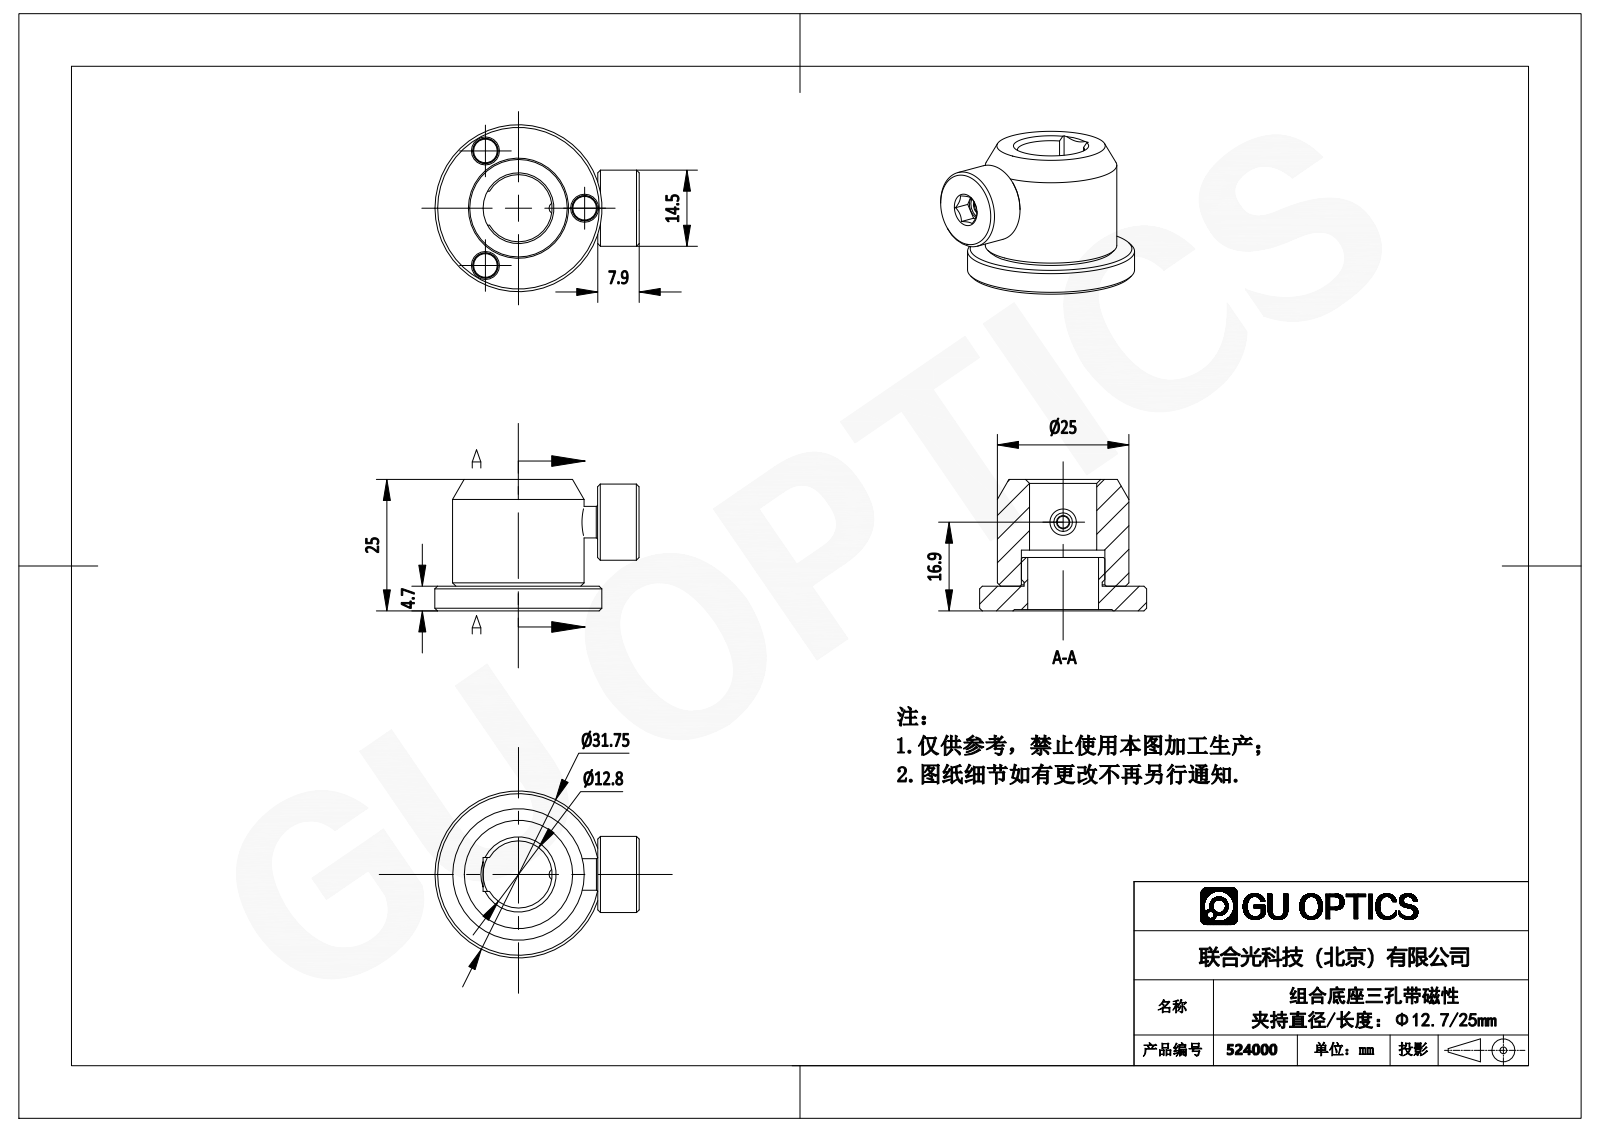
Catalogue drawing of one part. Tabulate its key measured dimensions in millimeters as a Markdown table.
| quantity | value |
| --- | --- |
| part name | 524000 |
| STEP written by | SolidWorks 2016 (AUTOMOTIVE_DESIGN) |
| units | millimeters |
| bodies | 9 solids, 183 faces (55 planar, 69 cylindrical, 59 other) |
| overall size | 38.82 × 31.75 × 25 |
| volume | 11 017 mm³ |
| surface area | 7 103 mm² |
| round holes (diameter × count) | 4.83 × 3, 2.15 × 1, 2.54 × 1, 3.17 × 1, 3.51 × 1, 4.85 × 1, 5 × 1, 10.29 × 1, 12.78 × 1, 13.46 × 1, 15.88 × 1 |
| round bosses / shafts (diameter × count) | 4.76 × 3, 31.75 × 1, 25 × 1, 14.86 × 1, 14.48 × 1, 10.03 × 1, 6 × 1, 3.48 × 1 |
| main face-to-face distances | 4.7, 25, 20.3, 4.44, 24.74, 7.87, 21.81, 29.68, 11.56, 11.3 |
| hole center spacings | 21.78, 12.58, 12.57 |
